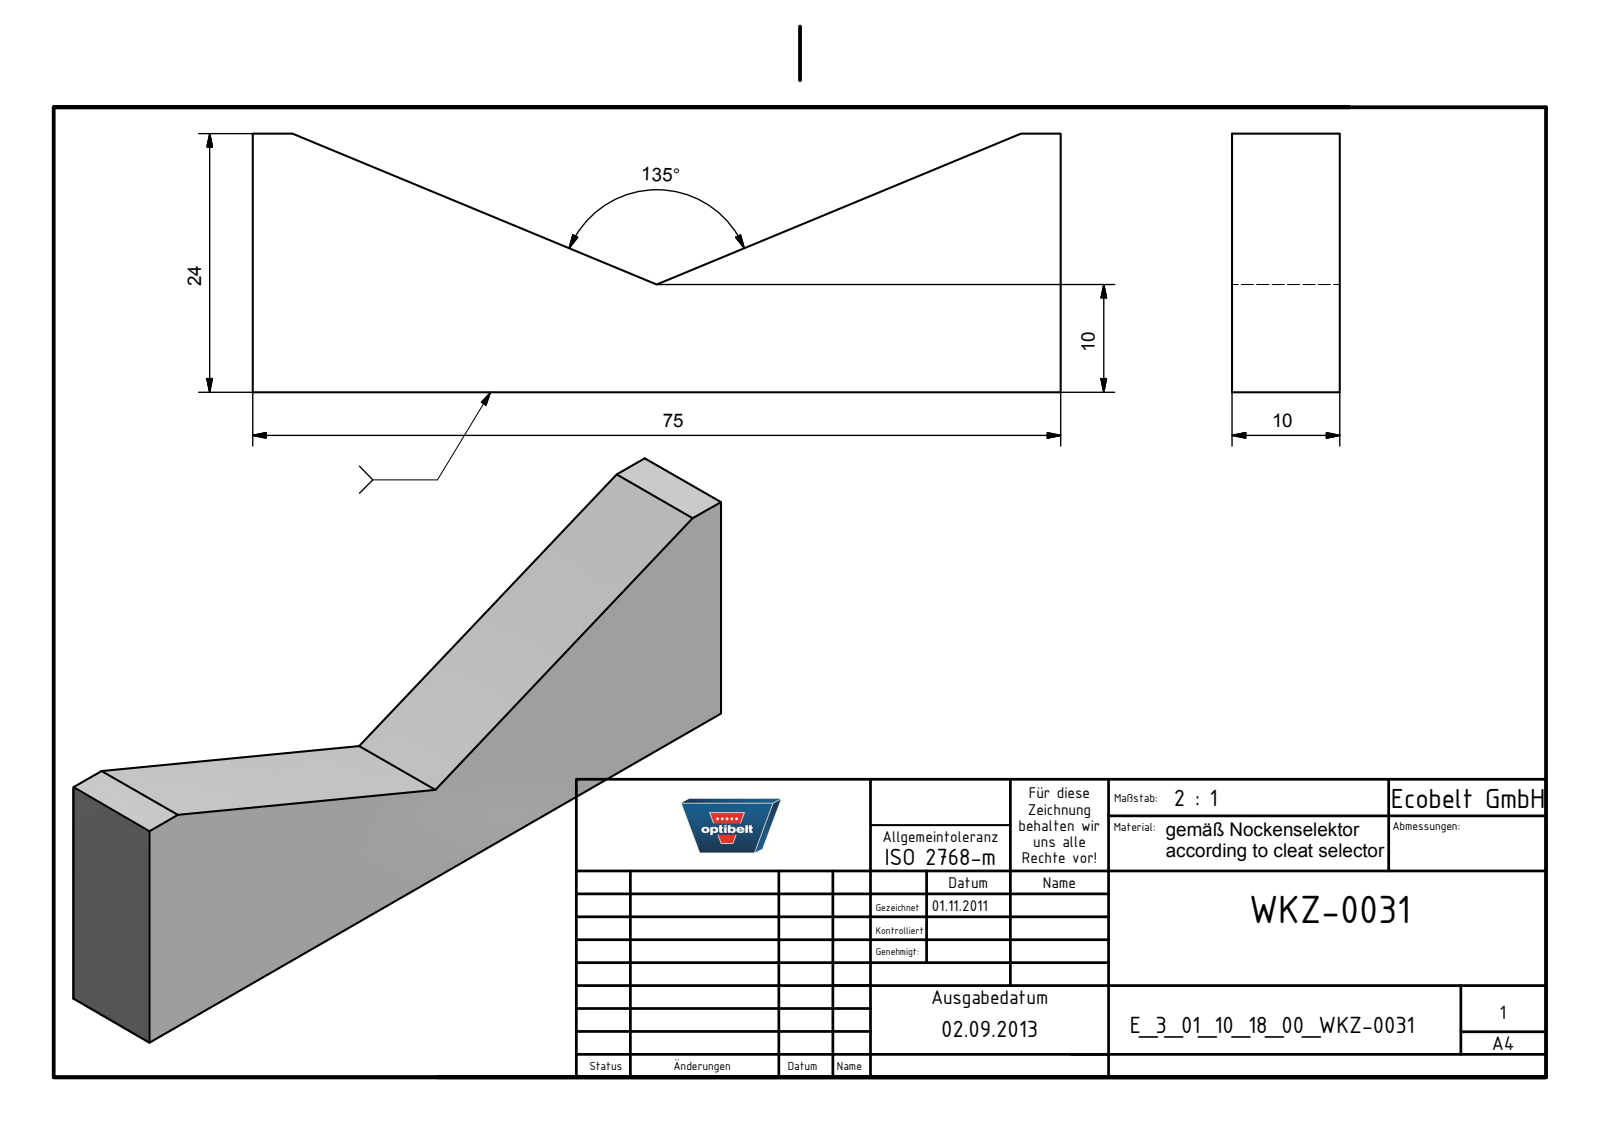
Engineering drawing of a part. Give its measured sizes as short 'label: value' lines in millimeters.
name: E_3_01_10_18_00_WKZ-0031
written by: Autodesk Inventor 2021 (AUTOMOTIVE_DESIGN)
unit: mm
bodies: 1 solid, 9 faces (9 planar, 0 cylindrical, 0 other)
size: 75 × 24 × 10
volume: 13 268 mm³; area: 4 689 mm²
face distances: 10, 75, 24
